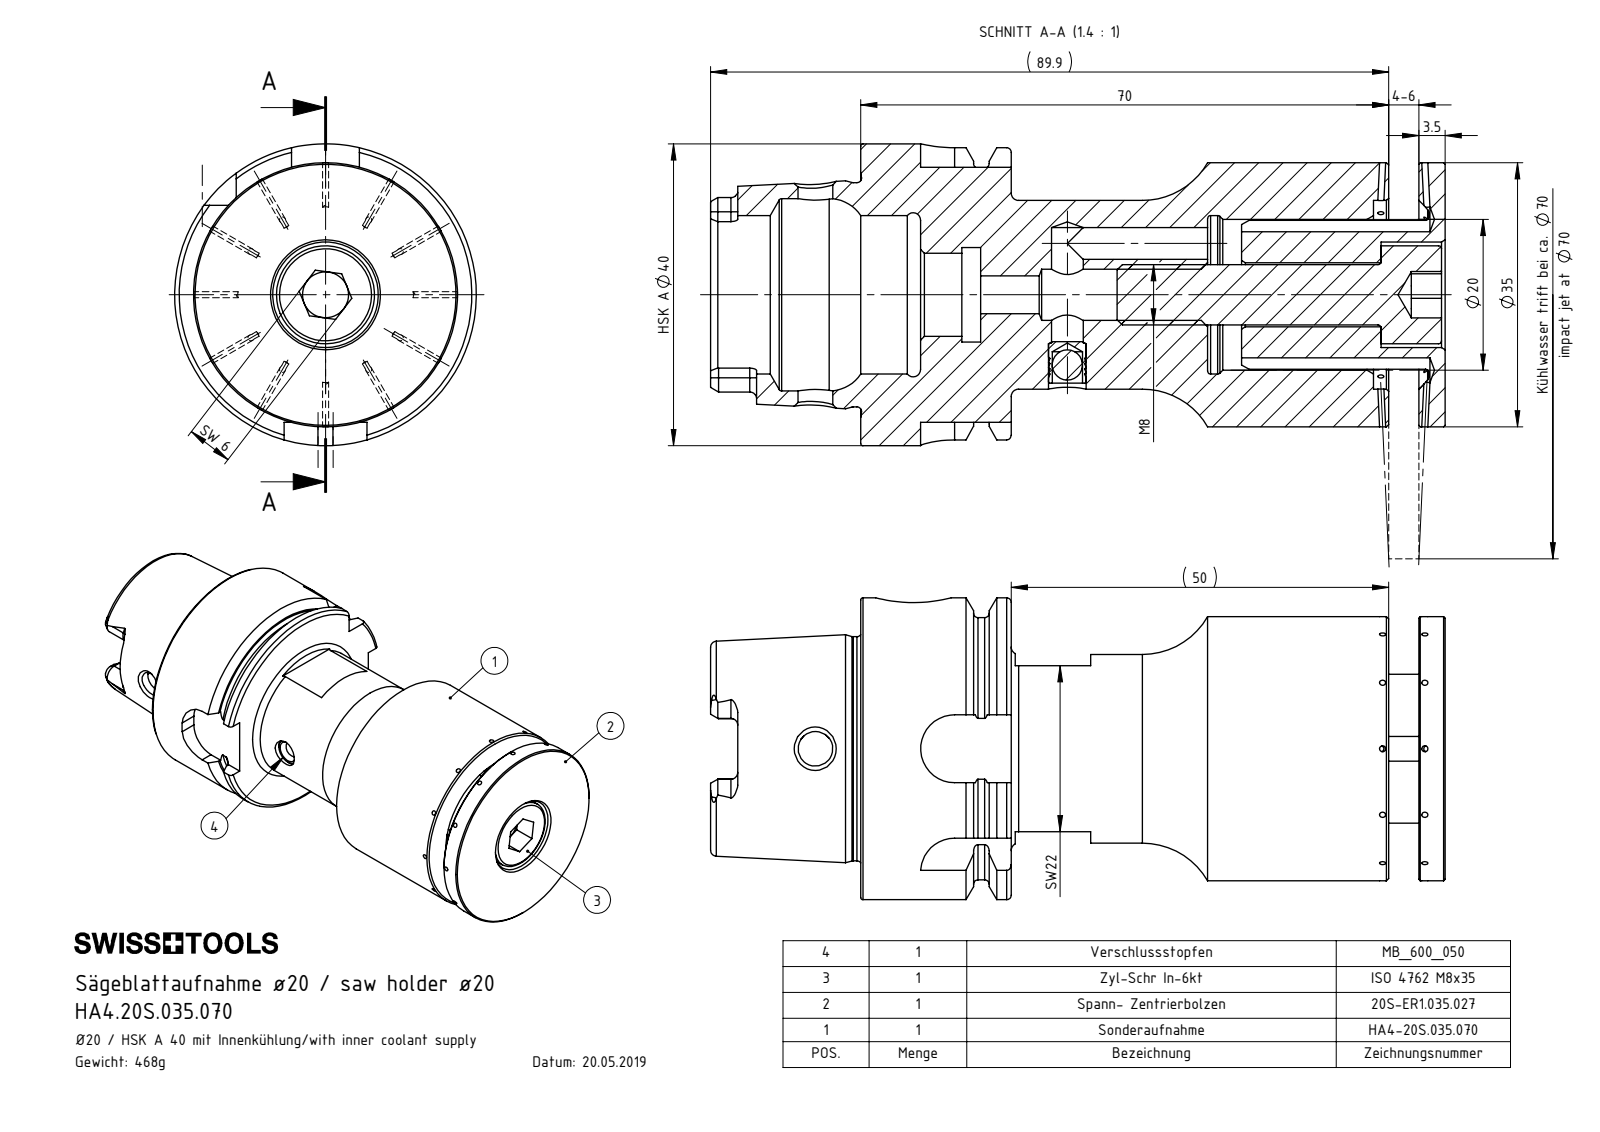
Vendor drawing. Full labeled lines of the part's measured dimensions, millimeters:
Part name (STEP PRODUCT): HA4.20S.035.070; HA4-20S.035.070_A_Fertigbearbeitung; 20S-ER1.035.027_A; KVT_MB_600_050 (+1 more)
STEP written by: SolidWorks 2017 (AUTOMOTIVE_DESIGN)
Units: millimetres
Bodies: 5 solids, 272 faces (85 planar, 81 cylindrical, 106 other)
Overall size (bounding box): 97.4 × 40 × 40
Volume: 61 931 mm³ · Surface area: 24 237 mm²
Round holes (diameter × count): ⌀0.8 ×24, ⌀3.3 ×4, ⌀4.2 ×2, ⌀4 ×1, ⌀4.6 ×1, ⌀5 ×1, ⌀6.8 ×1, ⌀8.5 ×1, ⌀10 ×1, ⌀11 ×1, ⌀12.5 ×1, ⌀14 ×1
Round bosses / shafts (diameter × count): ⌀40 ×1, ⌀35 ×1, ⌀34.75 ×1, ⌀29.71 ×1, ⌀20 ×1, ⌀13 ×1, ⌀8 ×1, ⌀5 ×1
Partial cylindrical surfaces — rounded edges, fillets, slot ends (radius × count): R0.9 ×6, R1.88 ×4, R4.5 ×4
Main face-to-face distances: 57.55, 54.05, 3.5, 50.05, 4, 7.5, 19.95, 70, 74, 77.5
Hole centre spacings: 7.16, 10, 14.14, 12.09, 20, 3.2, 6.8, 16.8
